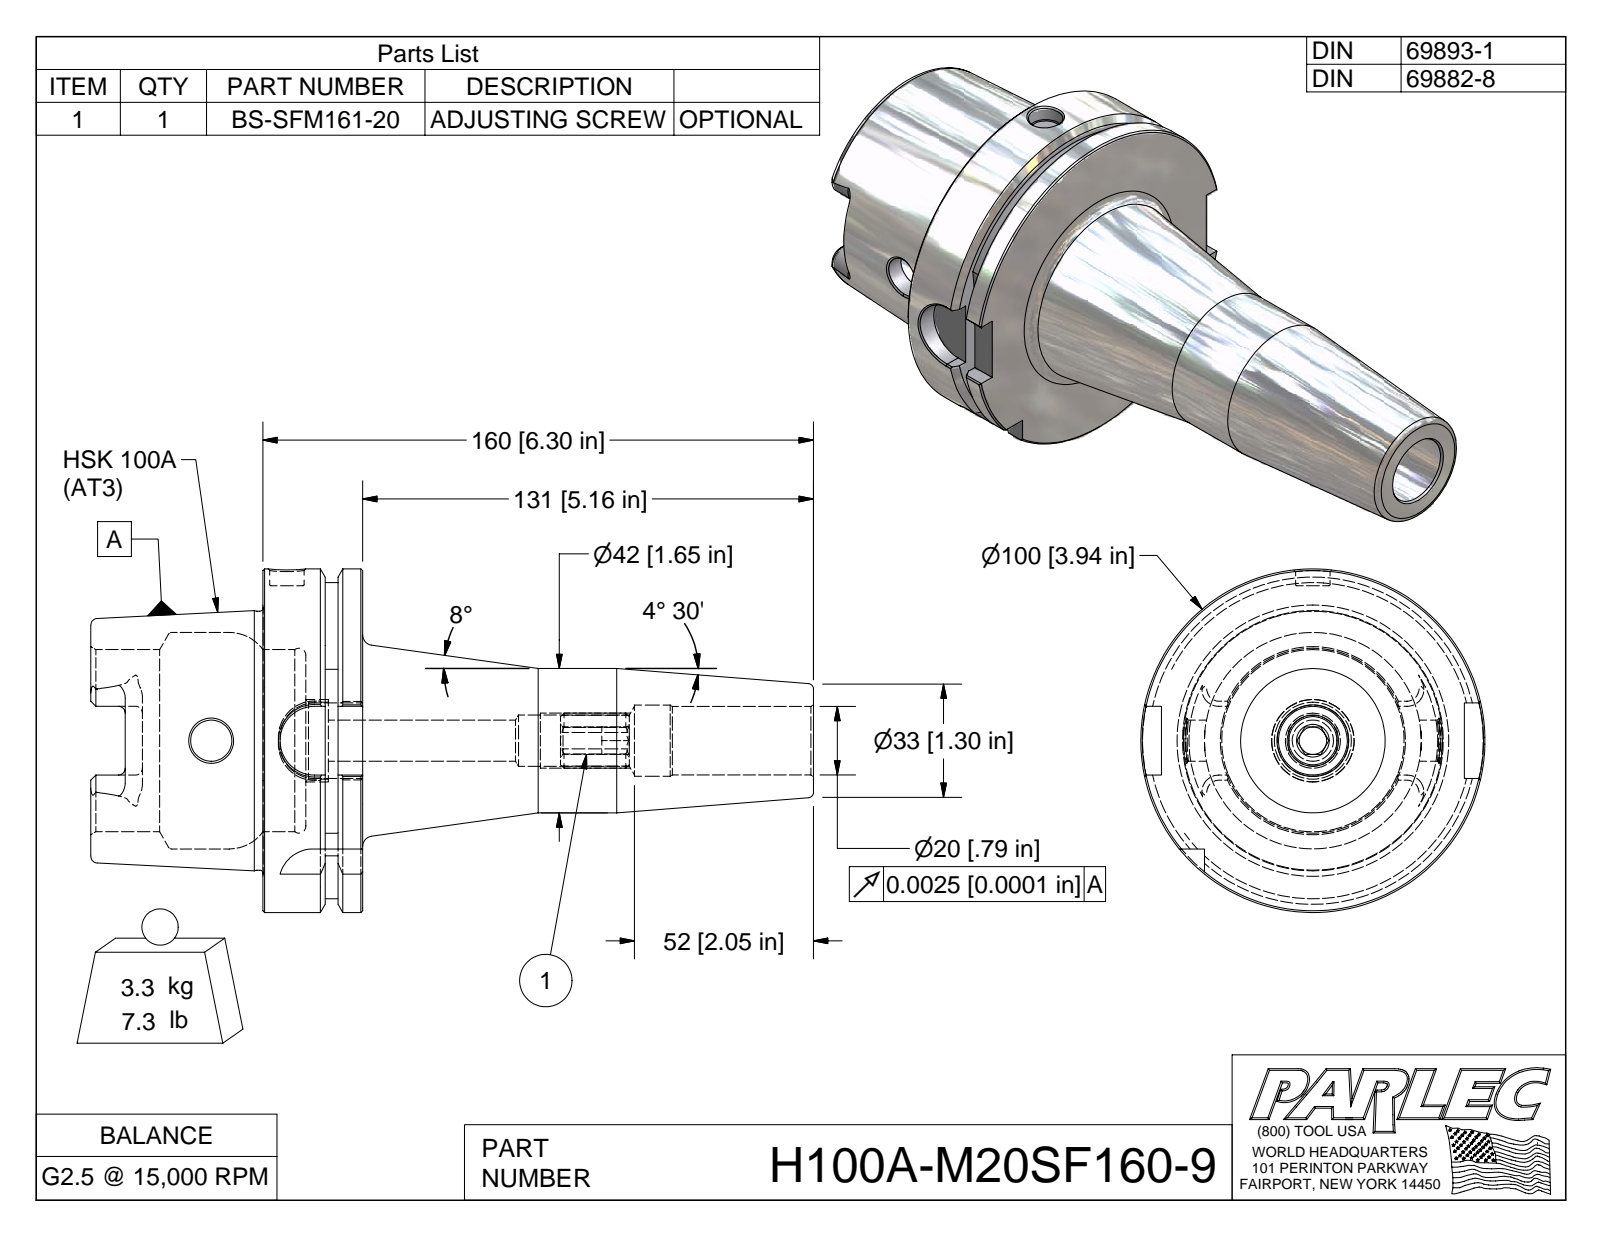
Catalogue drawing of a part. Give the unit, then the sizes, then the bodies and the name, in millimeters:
Units: millimetres
Overall size (bounding box): 210 × 100 × 100
Round holes (diameter × count): ⌀10 ×1, ⌀12 ×1, ⌀20 ×1, ⌀20.7 ×1, ⌀22.4 ×1, ⌀53 ×1, ⌀63 ×1
Round bosses / shafts (diameter × count): ⌀100 ×1, ⌀75.4 ×1, ⌀42 ×1
Partial cylindrical surfaces — rounded edges, fillets, slot ends (radius × count): R10 ×4, R2 ×3, R4.9 ×2, R8 ×1, R46 ×1
Main face-to-face distances: 29, 12.5, 16.5, 50, 62.5, 79, 68.1, 18.1, 5.6, 10.9
Volume: 424 400 mm³ · Surface area: 73 480 mm²
Bodies: 2 solids, 148 faces (48 planar, 29 cylindrical, 71 other)
Part name (STEP PRODUCT): H100A-M20SF160-9; H100A-M20SF160-9-1; BS-SFM161-20
STEP written by: Autodesk Inventor 2009 (AUTOMOTIVE_DESIGN)
